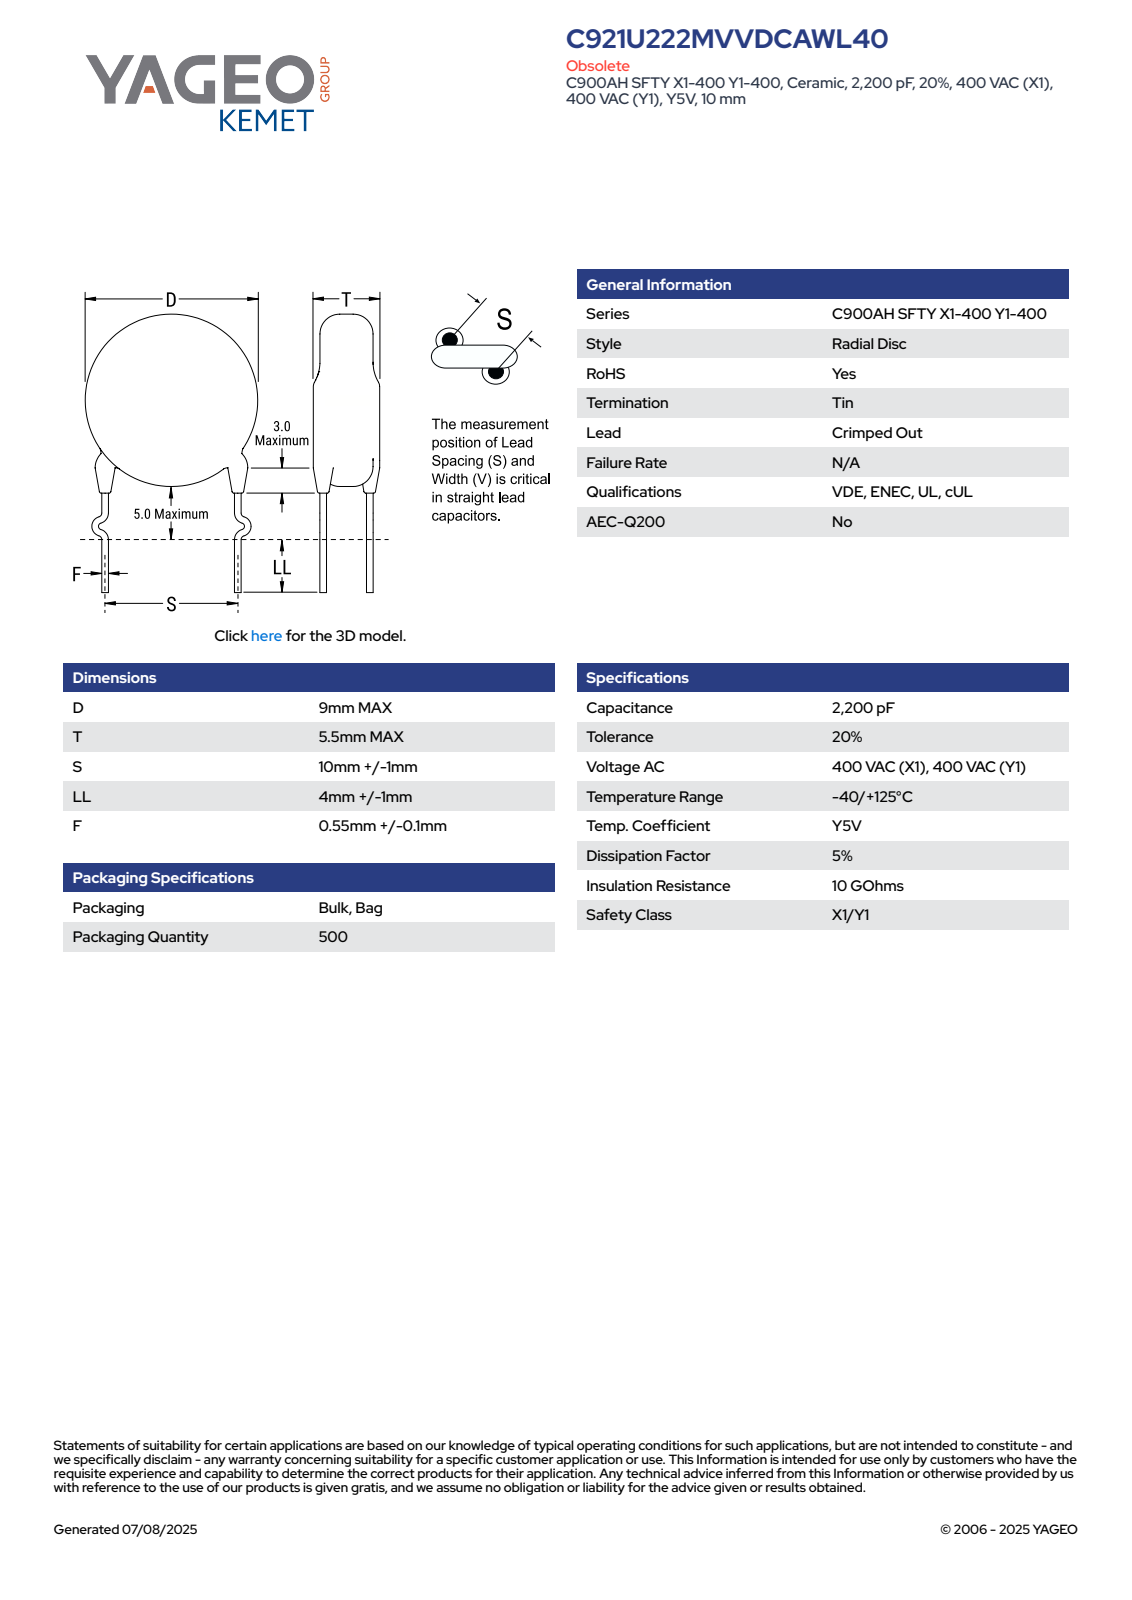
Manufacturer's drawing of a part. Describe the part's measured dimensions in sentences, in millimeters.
The part is named "CCD_KCOC900_D9T5.5S10LL5F0.55". Its 3-D file was written by "SolidWorks 2014 (AUTOMOTIVE_DESIGN)". It is 4 solids with 93 faces: 63 planar, 10 cylindrical and 20 other. Overall it measures 19 by 14.29 by 6.24 millimeters. Its volume is 354 cubic millimeters and its surface area 338 square millimeters. Round bosses or shafts: 2 of diameter 1.2, 1 of diameter 9. Partial cylindrical surfaces (rounded edges, fillets, slot ends): 2 of radius 0.6. The main face-to-face distances are 5.5, 0.94, 4.98, 4.04, 0.76, 3.82, 0.58, 4.07, 2.77, 2.88.
